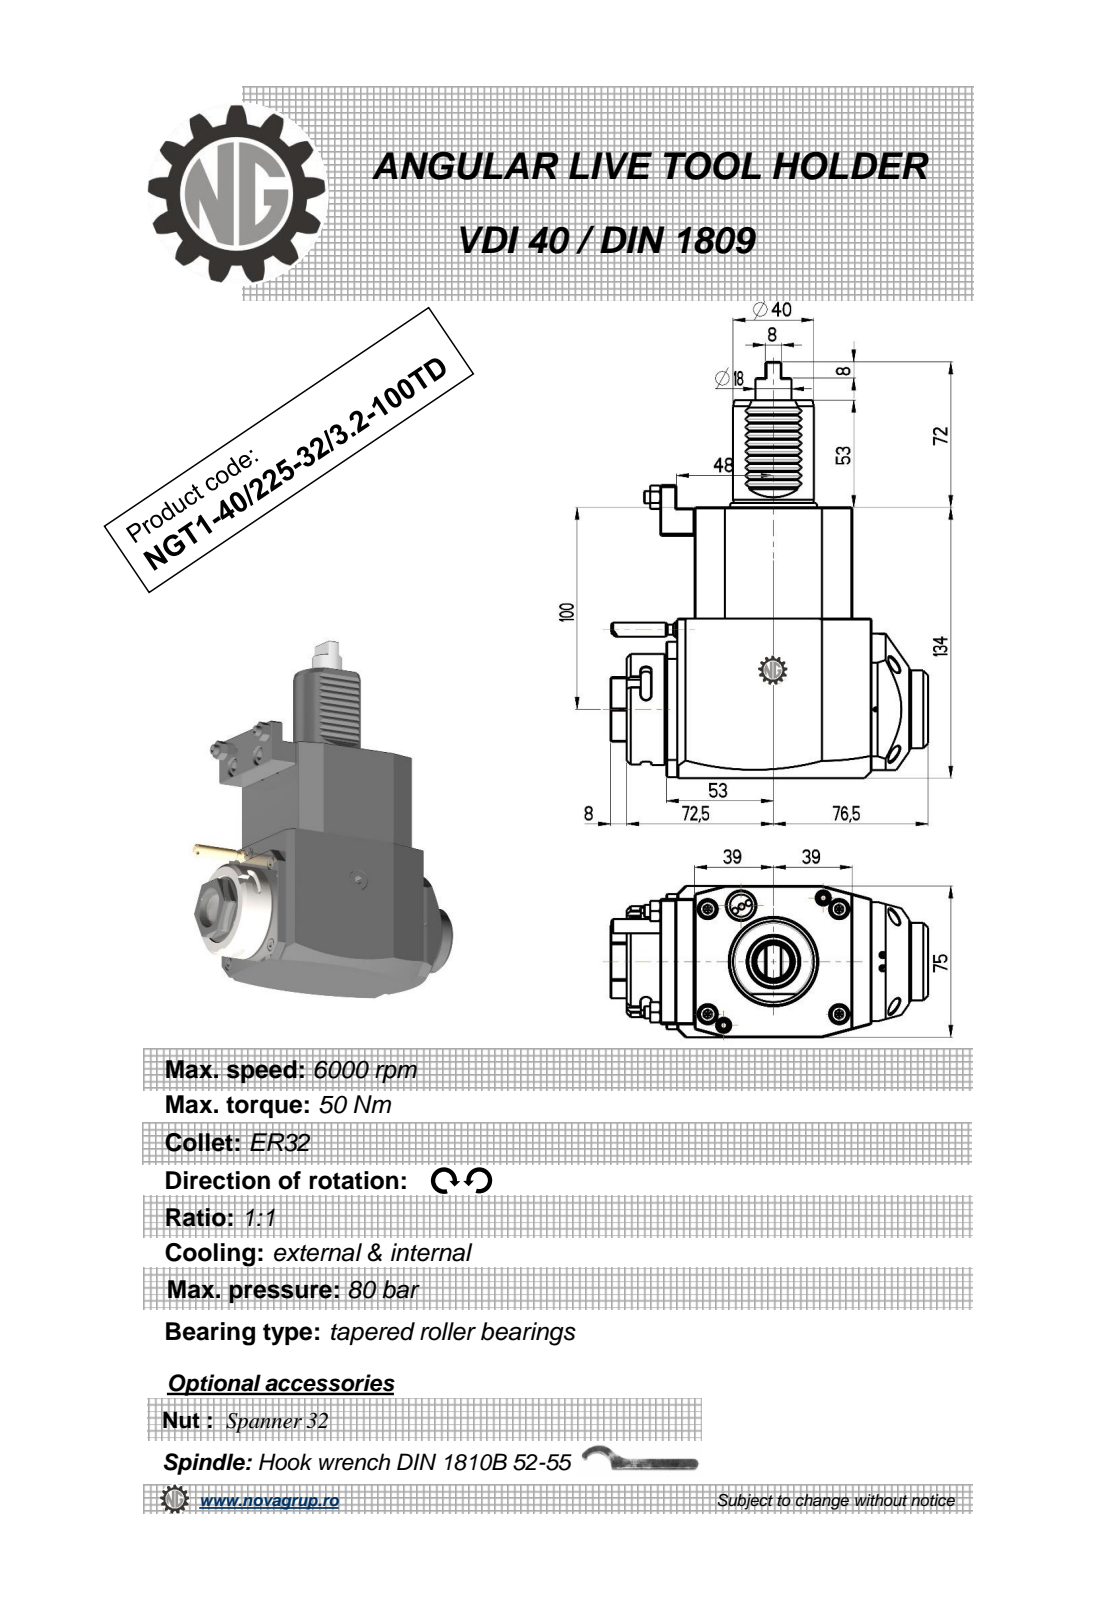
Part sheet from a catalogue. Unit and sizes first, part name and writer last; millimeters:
Units: millimetres
Overall size (bounding box): 206 × 157 × 75
Round holes (diameter × count): ⌀2 ×2, ⌀2.6 ×2, ⌀2.5 ×1, ⌀3 ×1, ⌀23 ×1
Round bosses / shafts (diameter × count): ⌀40 ×2, ⌀6 ×2, ⌀55 ×1, ⌀48 ×1, ⌀38.5 ×1, ⌀17.8 ×1, ⌀8 ×1, ⌀7 ×1
Partial cylindrical surfaces — rounded edges, fillets, slot ends (radius × count): R0.3 ×10, R0.31 ×10, R0.2 ×6, R2.5 ×6, R0.8 ×2, R180 ×2, R0.5 ×1, R24.5 ×1
Main face-to-face distances: 75, 134, 14, 78, 92, 0.5, 8.5, 19.5, 84.88, 8
Hole centre spacings: 14.25, 28.5, 39.63, 43.2, 50.68
Volume: 1 091 000 mm³ · Surface area: 79 418 mm²
Bodies: 1 solid, 378 faces (194 planar, 80 cylindrical, 104 other)
Part name (STEP PRODUCT): NGT1_40_225_32_3_2_100TD
STEP written by: PRO/ENGINEER BY PARAMETRIC TECHNOLOGY CORPORATION, 2010280 (CONFIG_CONTROL_DESIGN)
